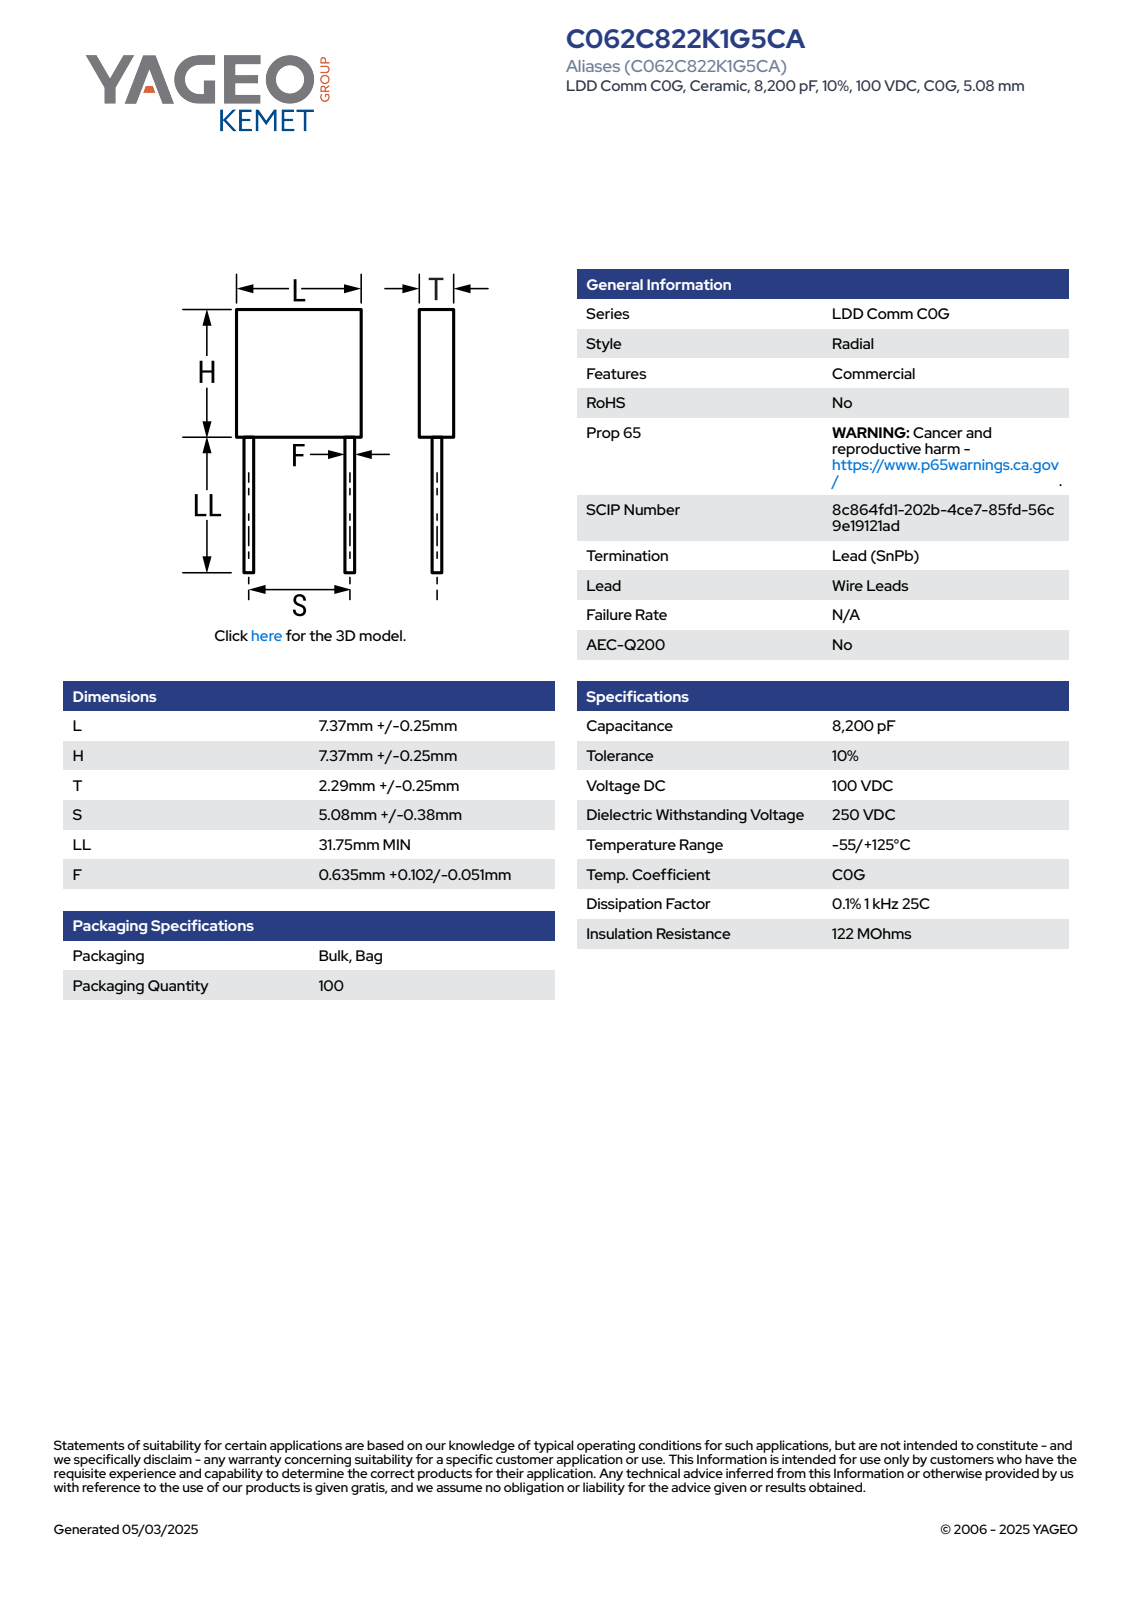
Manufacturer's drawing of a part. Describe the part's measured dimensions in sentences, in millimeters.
The part is named "CCR_RMST_C062_L7.62H7.62T2.54S8.89LL31.75F0.735". Its 3-D file was written by "SolidWorks 2014 (AUTOMOTIVE_DESIGN)". It is 4 solids with 73 faces: 65 planar, 4 cylindrical and 4 other. Overall it measures 39.37 by 9.62 by 2.54 millimeters. Its volume is 174 cubic millimeters and its surface area 353 square millimeters. Round bosses or shafts: 2 of diameter 0.73. The main face-to-face distances are 2.54, 7.62, 31.75, 39.37, 3.13, 1.37, 36.24, 4.49, 34.87, 3.12.
